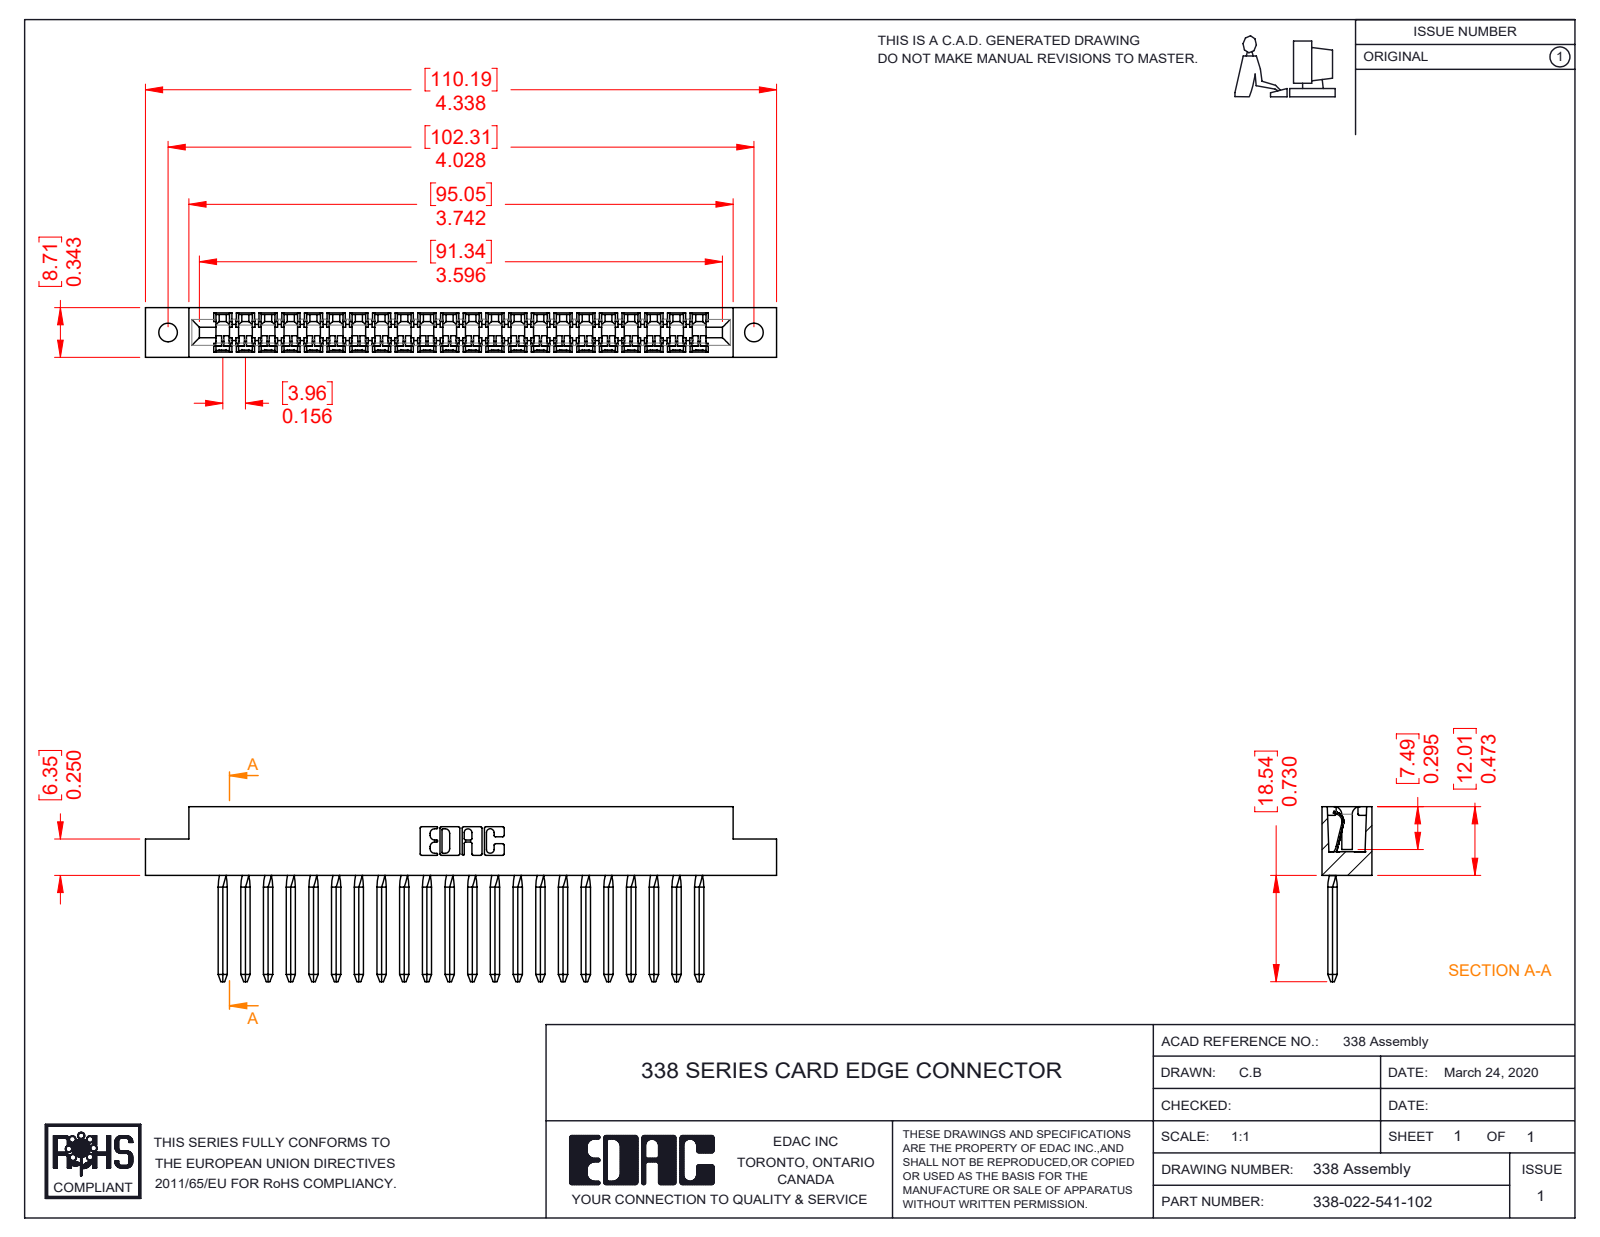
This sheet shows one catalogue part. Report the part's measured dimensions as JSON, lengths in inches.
{"part_name": "338-022-541-102; 338-210-001_338-210-022-002; 338-290-001_541", "step_written_by": "SolidWorks 2016 (CONFIG_CONTROL_DESIGN)", "units": "inches", "bodies": {"solids": 23, "faces": 2140, "planar": 1480, "cylindrical": 572, "other": 88}, "overall_size": [4.338, 1.203, 0.343], "volume_in3": 0.468, "surface_area_in2": 18.76, "round_holes": [[0.128, 2]], "partial_cylinders_radius": [[0.025, 90], [0.008, 22], [0.01, 22], [0.055, 18], [0.067, 18], [0.1, 17], [0.007, 6], [0.031, 6]], "face_to_face_distances": [0.343, 0.156, 0.11, 0.624, 0.207, 0.135, 0.78, 0.468, 0.221, 0.312], "hole_center_spacings": [4.028]}
